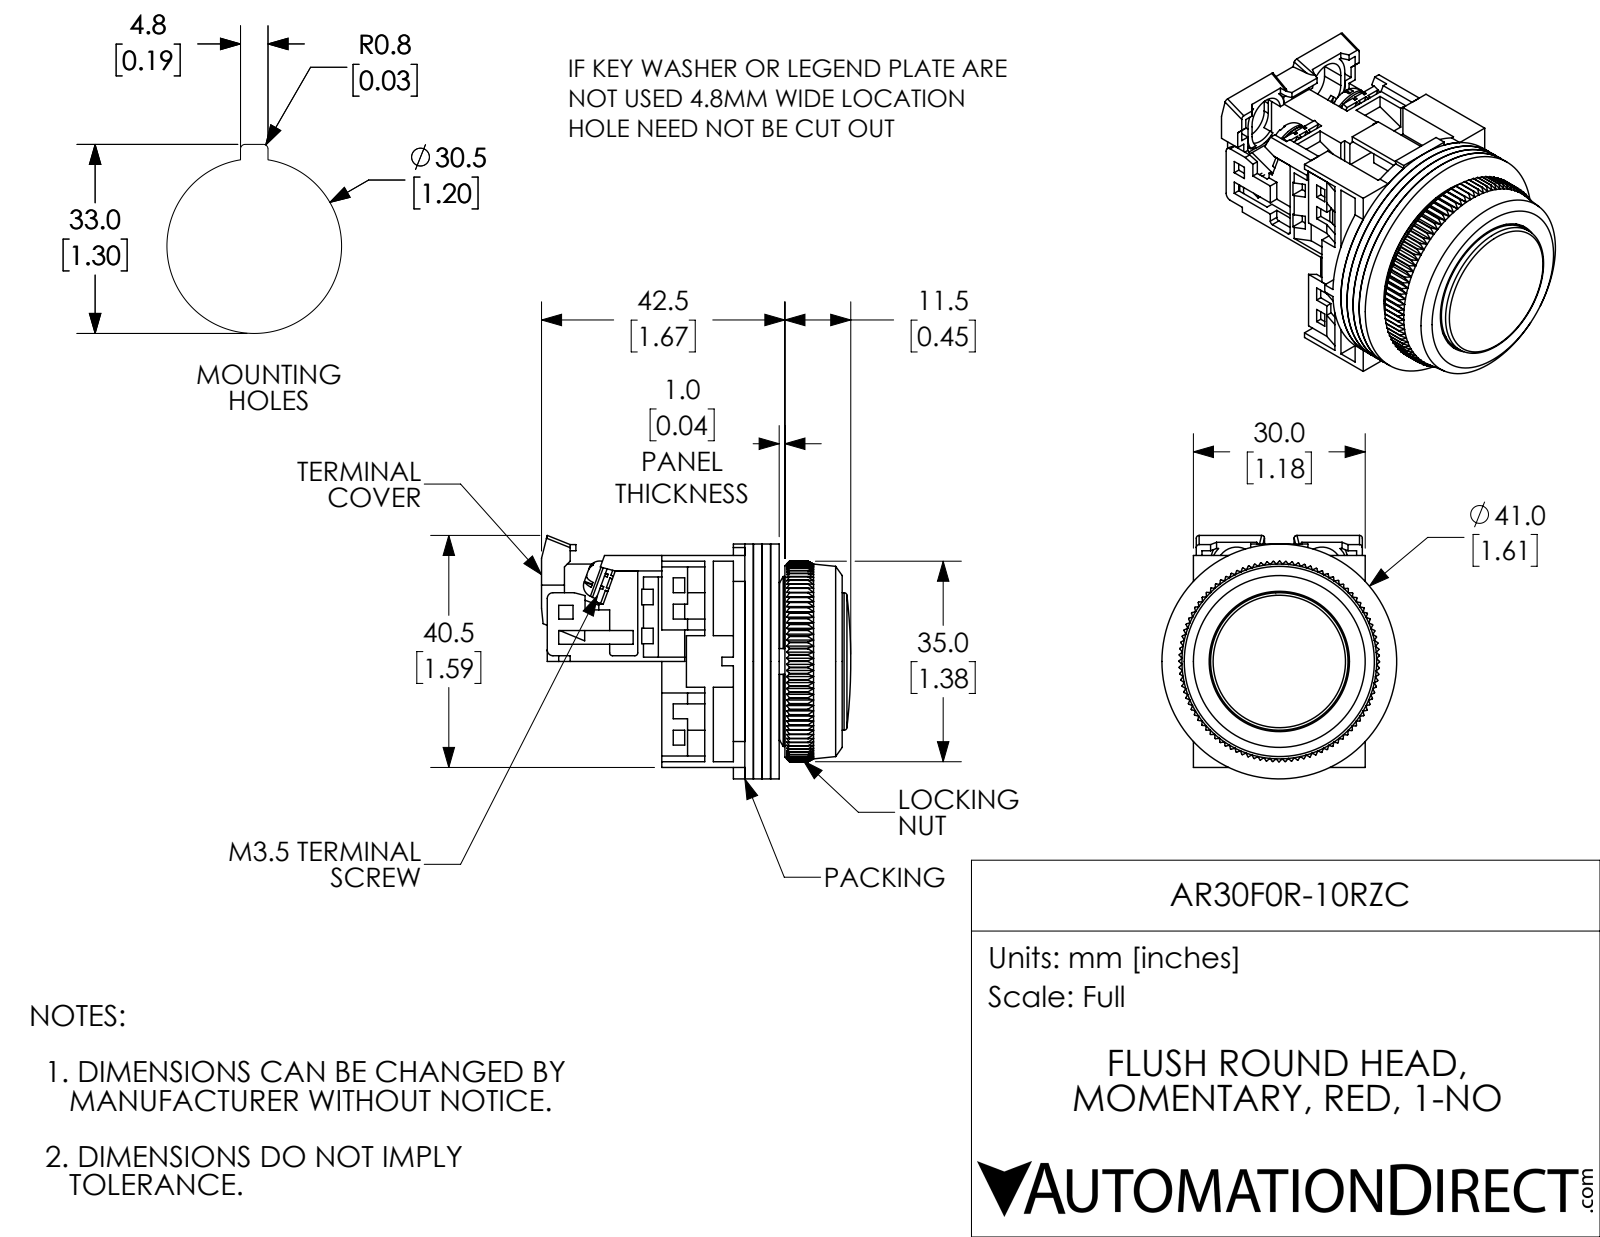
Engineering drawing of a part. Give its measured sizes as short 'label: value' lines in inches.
name: AR30F0R-10RZC
written by: SolidWorks 2017 (AUTOMOTIVE_DESIGN)
unit: in
bodies: 16 solids, 1258 faces (798 planar, 249 cylindrical, 211 other)
size: 2.125 × 1.673 × 1.614
volume: 1.595 in³; area: 47.89 in²
holes: 4× ⌀0.138, 2× ⌀0.142, 1× ⌀0.118, 1× ⌀0.472, 1× ⌀0.709, 1× ⌀0.787, 1× ⌀0.827, 1× ⌀0.945, 1× ⌀0.965, 1× ⌀1.122, 1× ⌀1.252
bosses: 2× ⌀0.26, 2× ⌀0.138, 1× ⌀1.614, 1× ⌀1.181, 1× ⌀0.906, 1× ⌀0.866, 1× ⌀0.551
rounds: 8× R0.059, 6× R0.02, 2× R0.039, 2× R0.138, 2× R0.177, 1× R0.118, 1× R0.398, 1× R0.449
face distances: 0.059, 0.118, 0.177, 0.039, 0.197, 0.079, 0.689, 1.417, 0.256, 0.138
hole spacings: 0.579, 0.61
